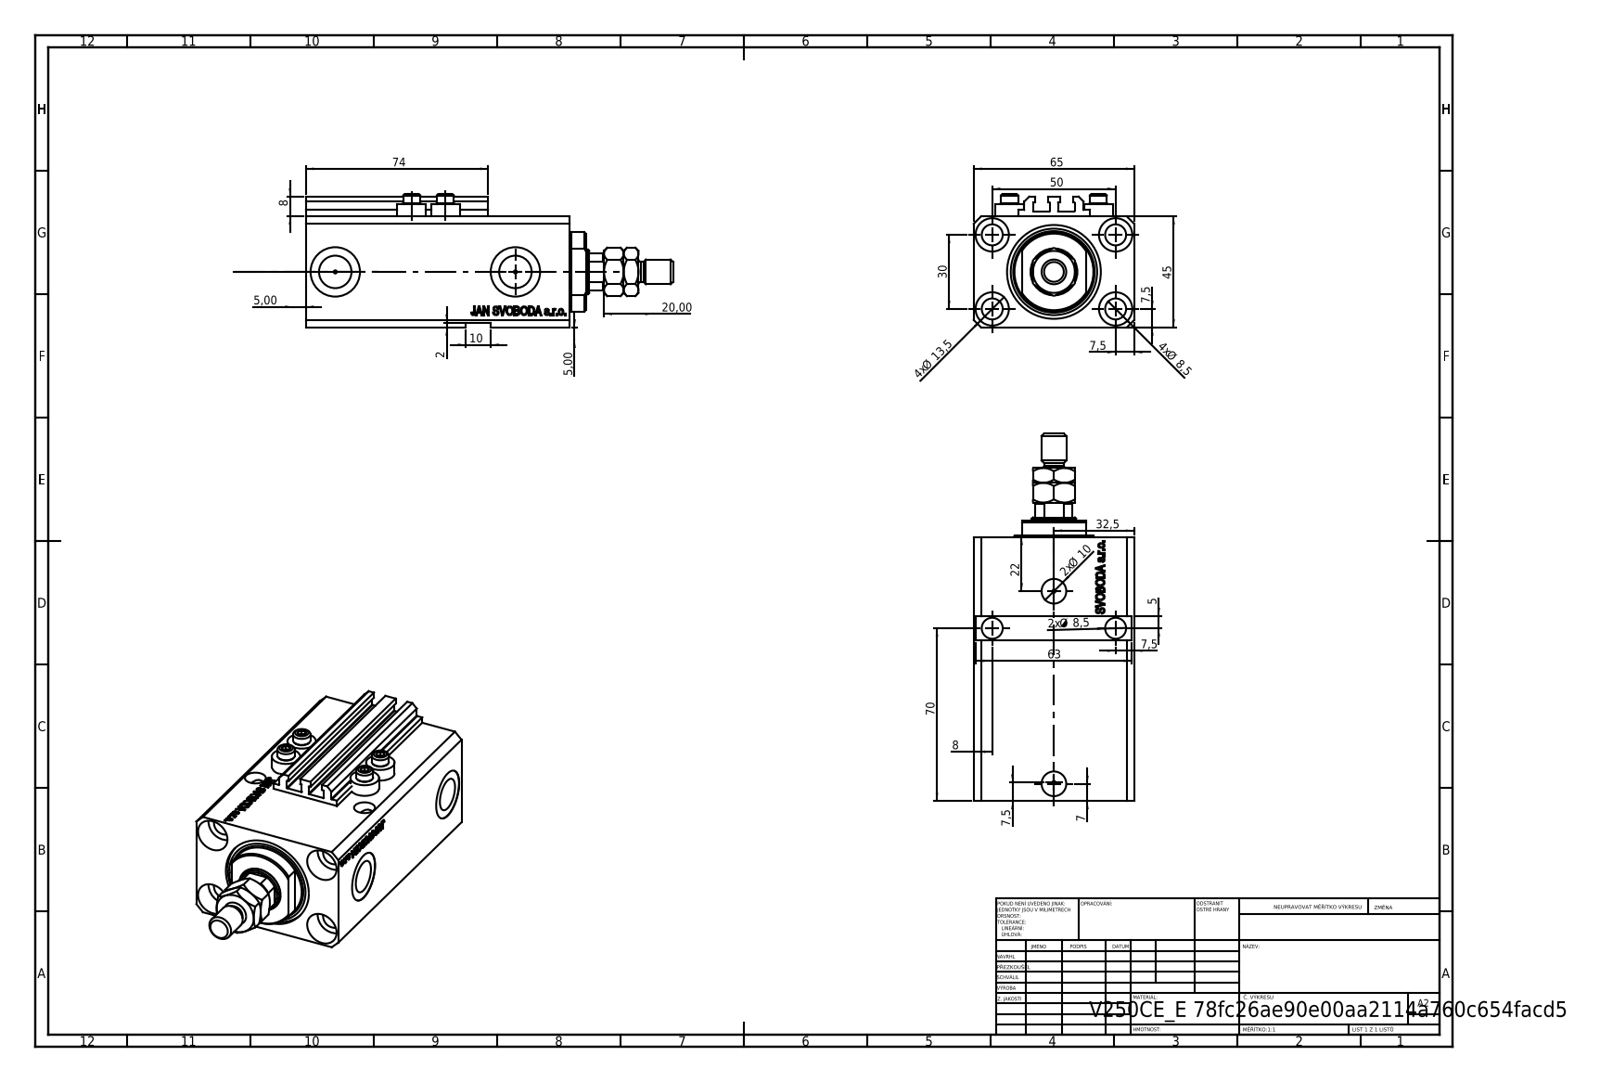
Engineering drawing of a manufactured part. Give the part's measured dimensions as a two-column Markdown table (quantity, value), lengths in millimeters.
| quantity | value |
| --- | --- |
| part name | V250CE_VC_E; ALLEN BOLT V250CE; V250CE_E_Body; V250CE_C_VCP (+1 more) |
| STEP written by | SolidWorks 2019 (CONFIG_CONTROL_DESIGN) |
| units | millimeters |
| bodies | 9 solids, 1132 faces (530 planar, 142 cylindrical, 460 other) |
| overall size | 148.9 × 65 × 54 |
| volume | 277 737 mm³ |
| surface area | 80 810 mm² |
| round holes (diameter × count) | 8.5 × 7, 1.25 × 4, 4 × 4, 13.5 × 4, 10 × 2, 13.16 × 2, 20 × 2, 18 × 1, 25 × 1, 38 × 1 |
| round bosses / shafts (diameter × count) | 11.6 × 4, 7 × 4, 10 × 1, 8 × 1 |
| partial cylindrical surfaces (radius × count) | 0.2 × 10, 8.5 × 1, 16 × 1 |
| main face-to-face distances | 45, 65, 81.9, 2, 47, 6.9, 107, 25.1, 24, 2.5 |
| hole center spacings | 29.15, 50, 13.6, 15.12, 27.89, 30, 33.62, 36 |
